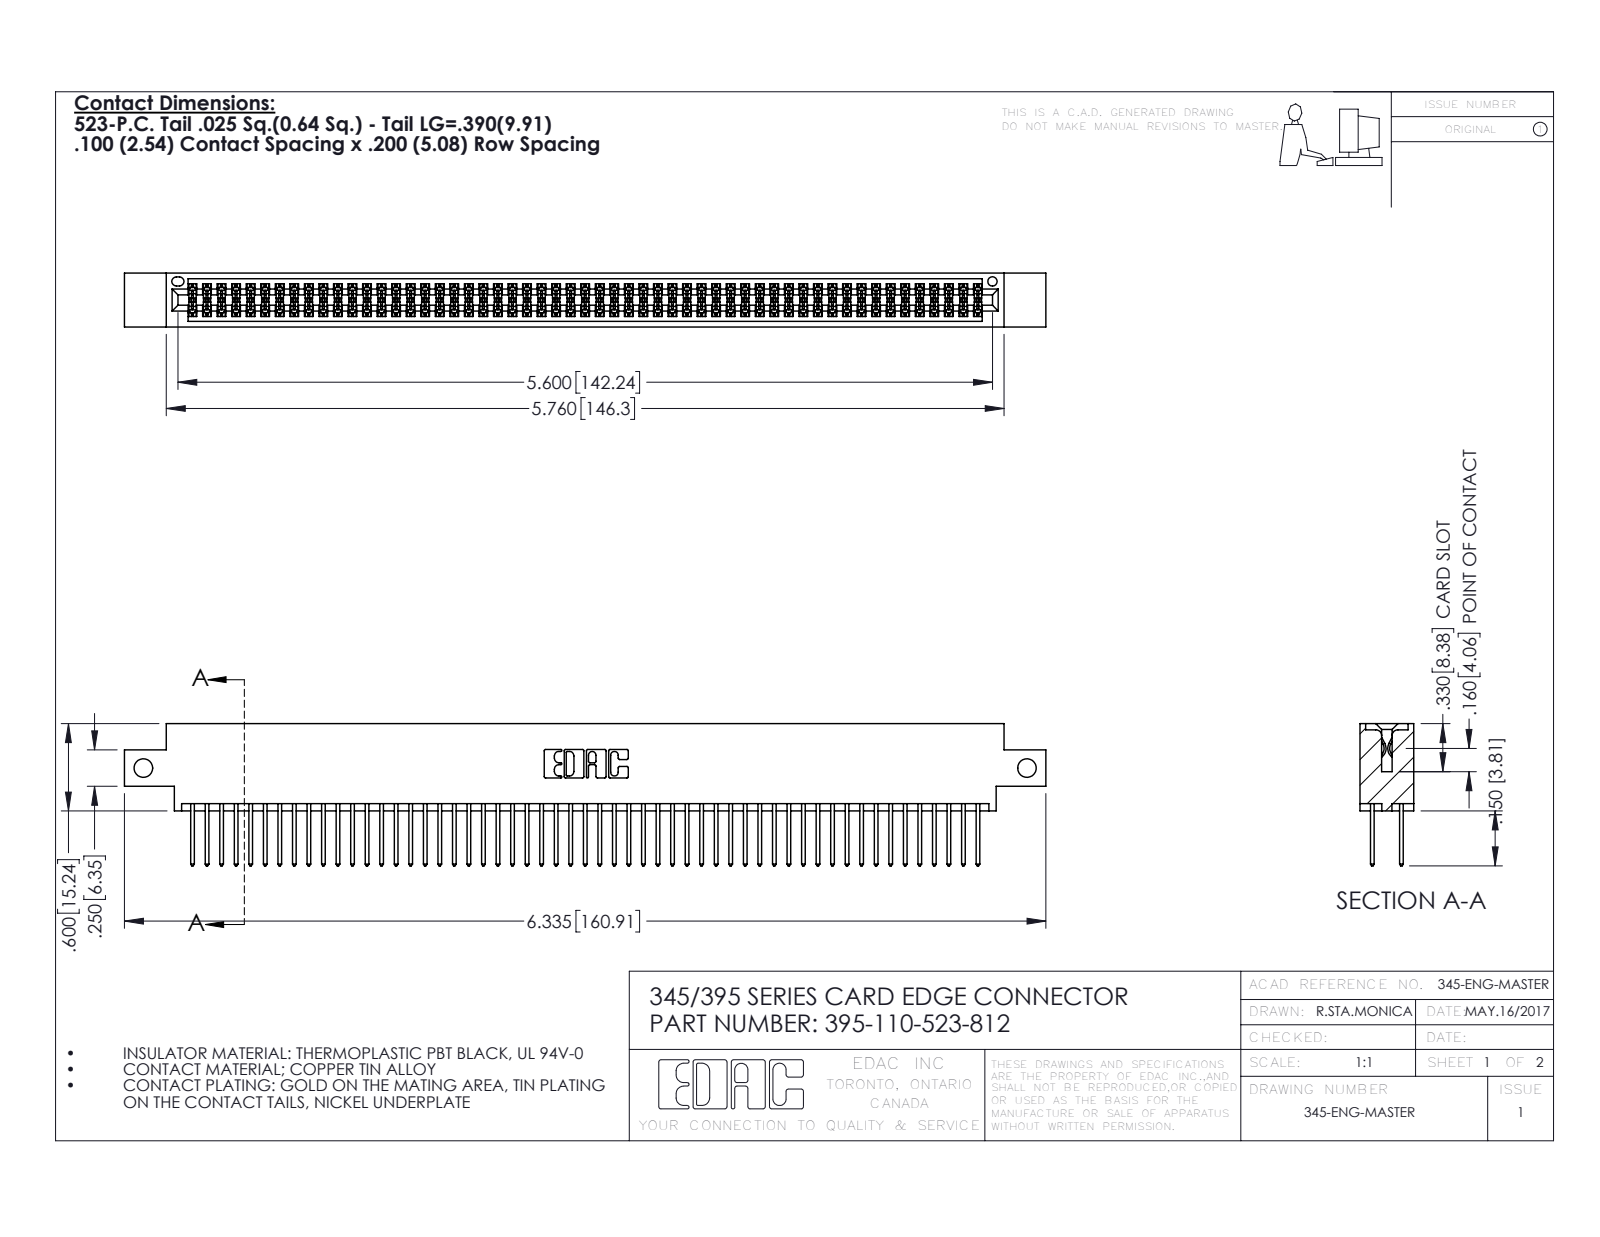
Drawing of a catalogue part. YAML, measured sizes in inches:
part_name: "345 Part_0.170 Offset - Side Mount; 395-110-523-812; 345-292-001_345-293-123"
step_written_by: "SolidWorks 2016 (CONFIG_CONTROL_DESIGN)"
units: inches
bodies: {solids: 111, faces: 5630, planar: 3714, cylindrical: 1916, other: 0}
overall_size: [6.335, 0.977, 0.37]
volume: 0.963
surface_area: 38.12
round_holes:
  - {diameter: 0.128, count: 2}
  - {diameter: 0.064, count: 1}
partial_cylinders:
  - {radius: 0.006, count: 165}
  - {radius: 0.01, count: 110}
  - {radius: 0.01, count: 22}
  - {radius: 0.007, count: 6}
  - {radius: 0.031, count: 6}
  - {radius: 0.026, count: 3}
  - {radius: 0.014, count: 2}
  - {radius: 0.019, count: 2}
face_to_face_distances: [0.072, 0.298, 0.2, 0.098, 0.272, 0.025, 0.37, 0.225, 0.175, 0.149]
hole_center_spacings: [6.075]
